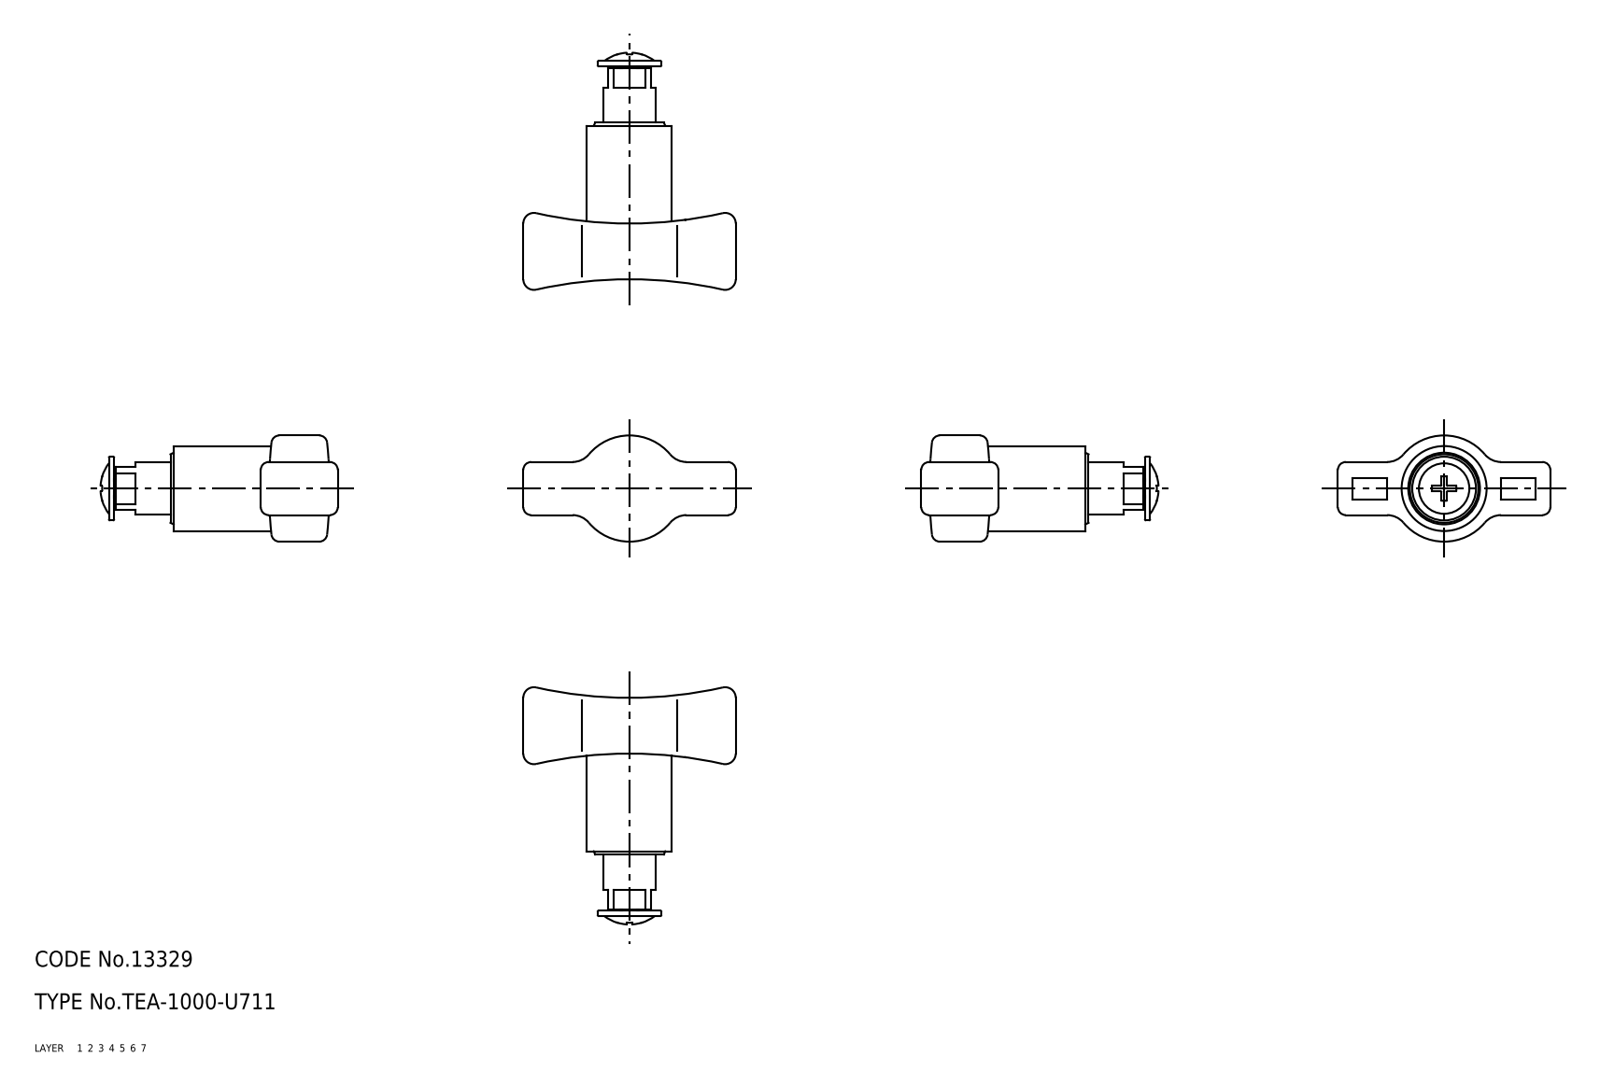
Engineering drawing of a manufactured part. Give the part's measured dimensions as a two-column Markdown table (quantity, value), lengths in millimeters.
| quantity | value |
| --- | --- |
| part name | shaft |
| STEP written by | CADfix (AUTOMOTIVE_DESIGN) |
| units | millimeters |
| bodies | 1 solid, 107 faces (0 planar, 0 cylindrical, 107 other) |
| overall size | 44.66 × 40 × 20 |
| volume | 10 227 mm³ |
| surface area | 4 094 mm² |
